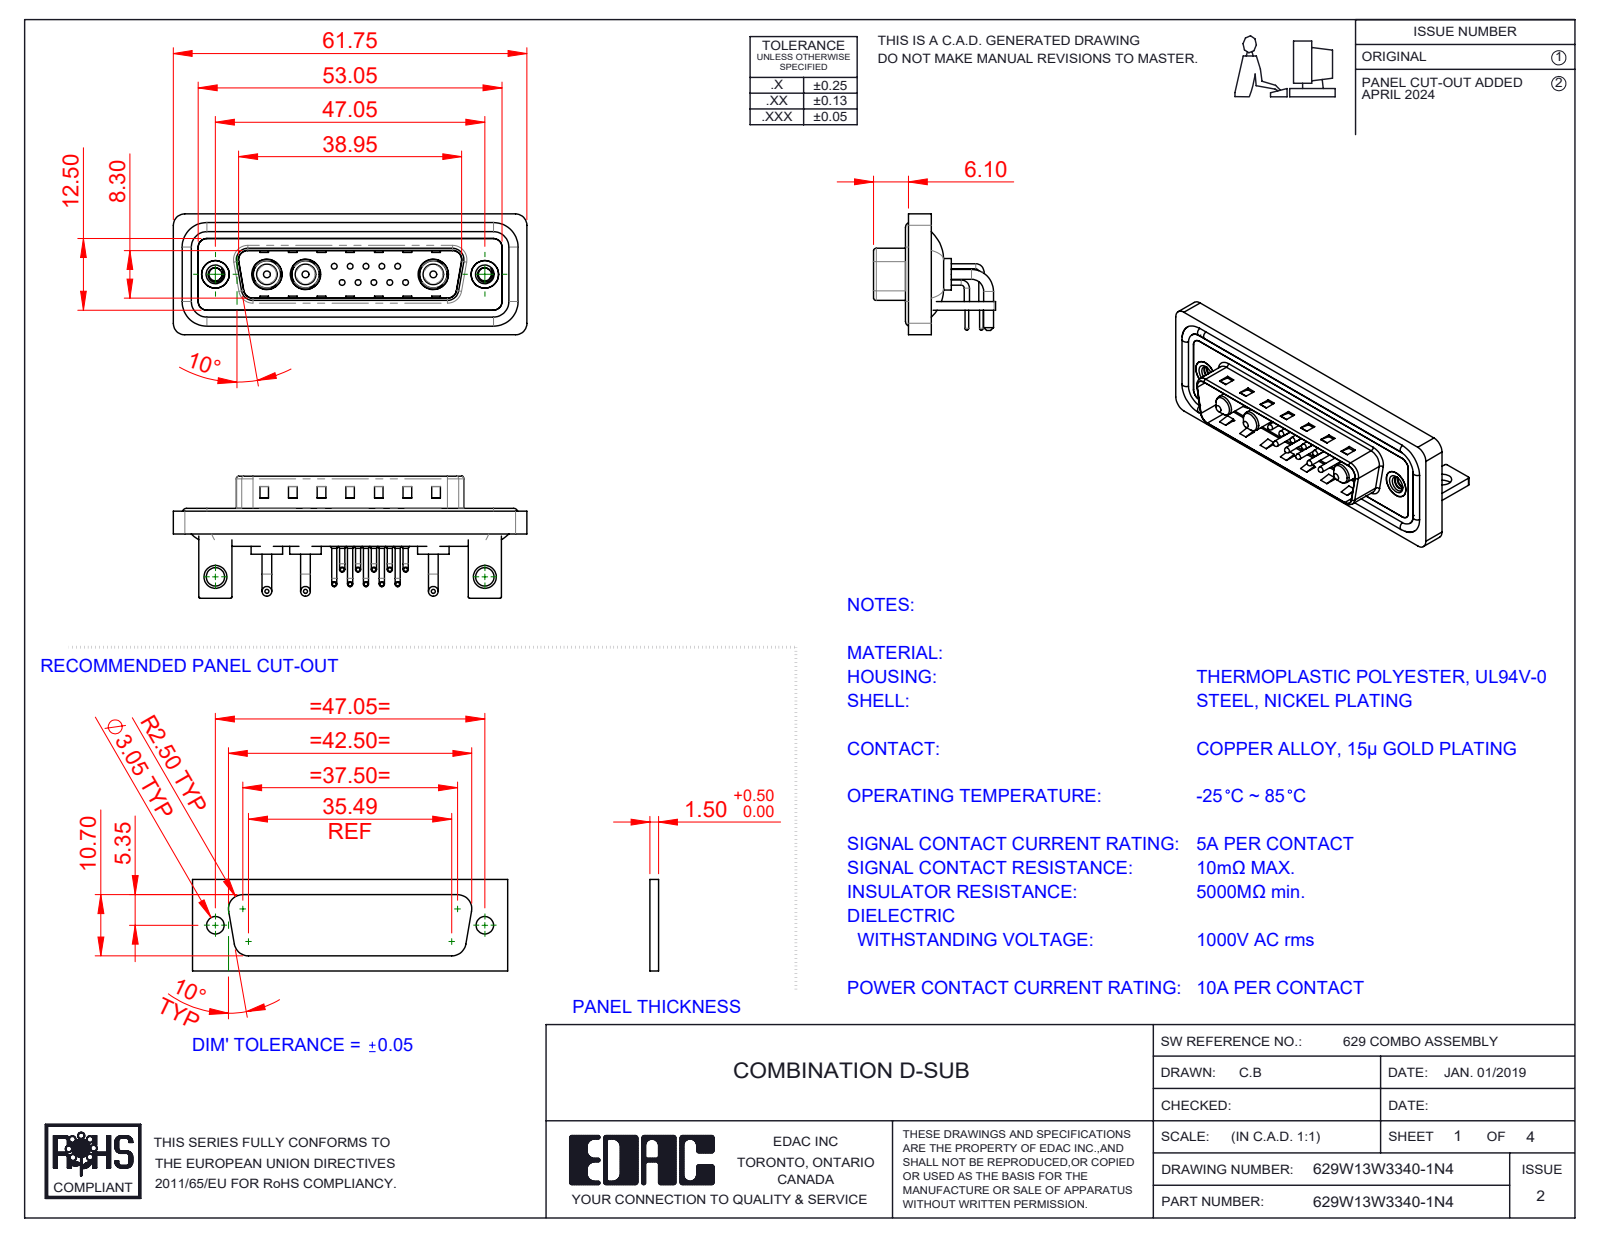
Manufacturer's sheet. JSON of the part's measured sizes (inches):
{"part_name": "629Combo Threaded Rivet_3; 629Combo Shell Front_25 Contacts; 629Combo Housing_13W3; 629Combo Stabilizer Bracket (+6 more)", "step_written_by": "SolidWorks 2023 (CONFIG_CONTROL_DESIGN)", "units": "inches", "bodies": {"solids": 25, "faces": 1752, "planar": 899, "cylindrical": 629, "other": 224}, "overall_size": [2.431, 0.839, 0.831], "volume_in3": 0.471, "surface_area_in2": 20.04, "round_holes": [[0.03, 10], [0.063, 10], [0.079, 10], [0.191, 3], [0.209, 3], [0.089, 2], [0.126, 2], [0.157, 2], [0.189, 2], [0.197, 2]], "round_bosses_or_shafts": [[0.035, 20], [0.059, 10], [0.039, 10], [0.026, 10], [0.067, 6], [0.063, 4], [0.217, 3], [0.205, 3]], "partial_cylinders_radius": [[0.079, 19], [0.059, 18], [0.01, 16], [0.04, 10], [0.02, 9], [0.063, 8], [0.024, 4], [0.026, 4]], "face_to_face_distances": [0.016, 0.059, 0.031, 0.114, 0.083, 0.043, 0.161, 0.063, 0.146, 0.177], "hole_center_spacings": [0.124, 0.109, 0.198, 0.218, 0.295, 0.198, 0.327, 0.398]}
